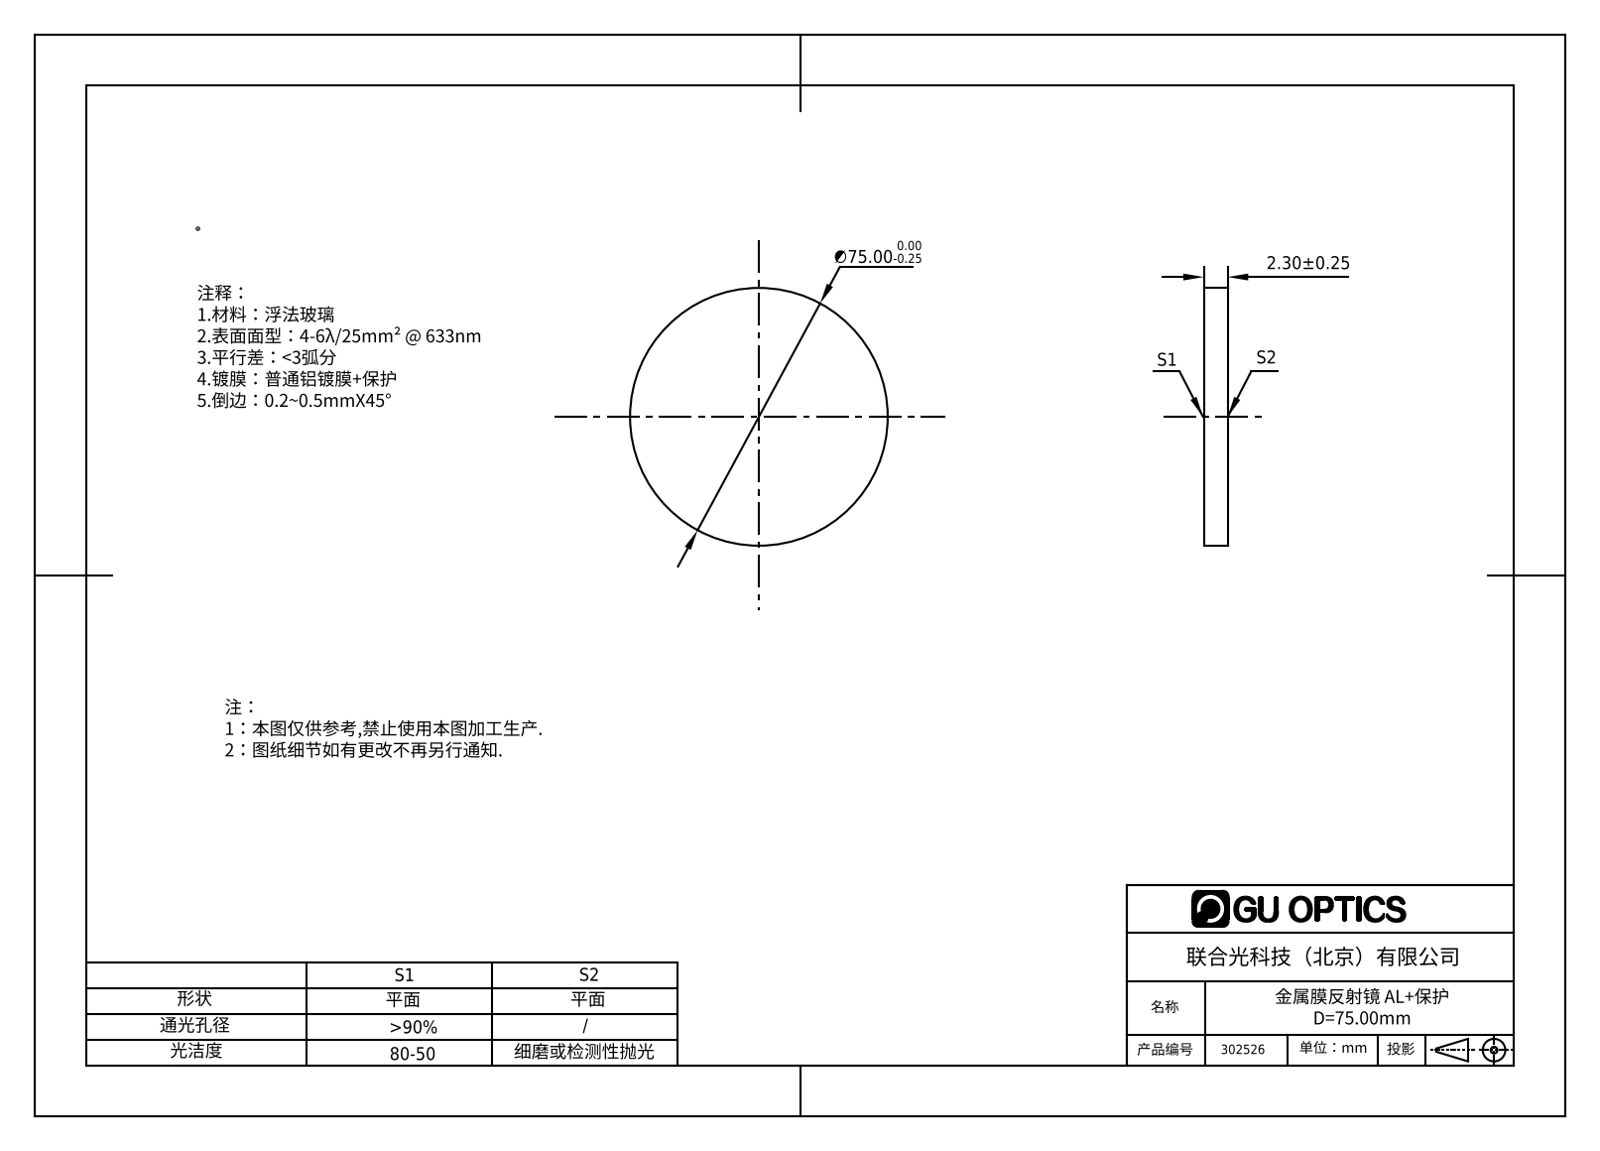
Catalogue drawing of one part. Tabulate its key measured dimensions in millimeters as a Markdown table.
| quantity | value |
| --- | --- |
| part name | 302526 |
| STEP written by | SolidWorks 2016 (AUTOMOTIVE_DESIGN) |
| units | millimeters |
| bodies | 1 solid, 4 faces (2 planar, 2 cylindrical, 0 other) |
| overall size | 75 × 75 × 2.3 |
| volume | 10 161 mm³ |
| surface area | 9 378 mm² |
| round bosses / shafts (diameter × count) | 75 × 1 |
| main face-to-face distances | 2.3 |
